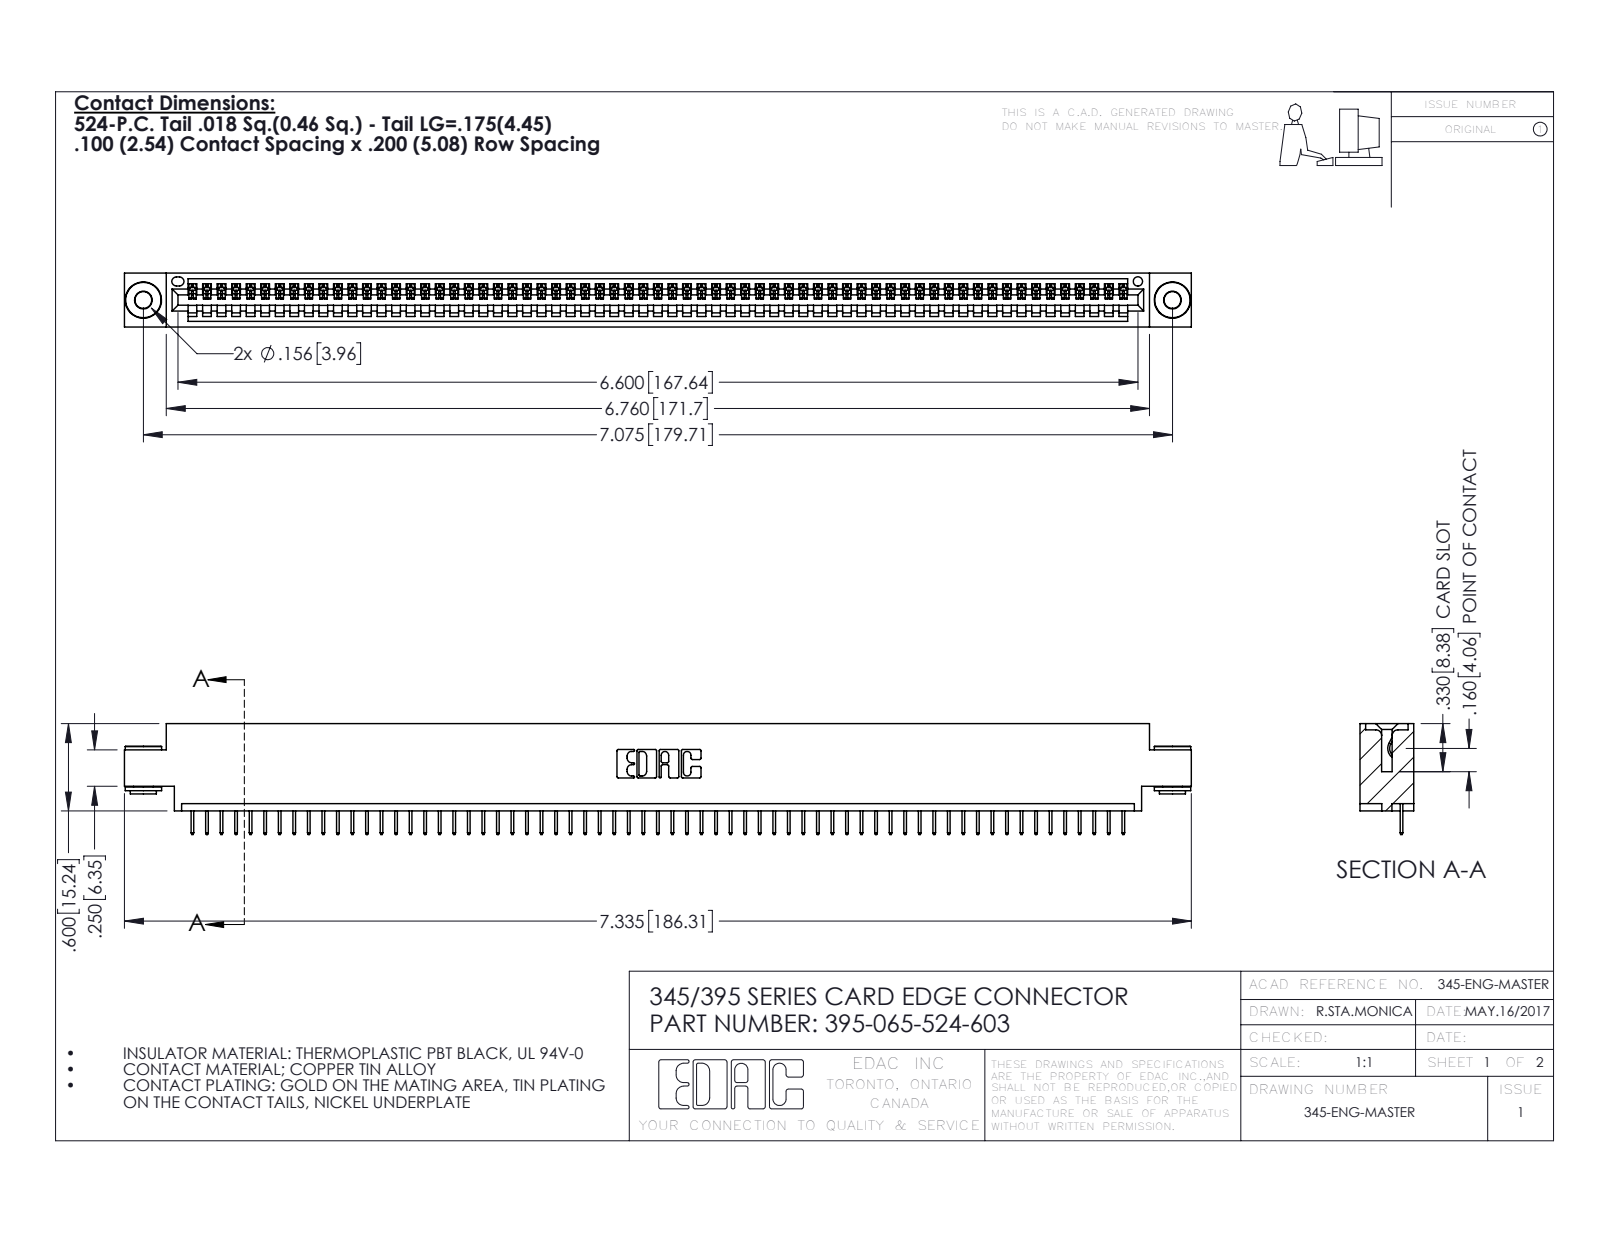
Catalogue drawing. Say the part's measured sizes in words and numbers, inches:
The part is named "345 Part_0.170 Offset - 0.156 Dia-TH; 345-250-002_345-250-002-102; 395-065-524-603; 345-292-001_345-293-124". Its 3-D file was written by "SolidWorks 2016 (CONFIG_CONTROL_DESIGN)". It is 68 solids with 4198 faces: 3084 planar, 1106 cylindrical and 8 other. Overall it measures 7.335 by 0.762 by 0.37 inches. Its volume is 1.07 cubic inches and its surface area 35.86 square inches. Round holes: 2 of diameter 0.116, 2 of diameter 0.156, 1 of diameter 0.064. Round bosses or shafts: 2 of diameter 0.25, 2 of diameter 0.18, 2 of diameter 0.136. Partial cylindrical surfaces (rounded edges, fillets, slot ends): 130 of radius 0.006, 22 of radius 0.01, 6 of radius 0.007, 6 of radius 0.031, 3 of radius 0.026, 2 of radius 0.031, 2 of radius 0.04, 1 of radius 0.014. The main face-to-face distances are 0.072, 0.298, 0.37, 0.2, 0.098, 0.272, 0.025, 0.225, 0.072, 0.175. The hole center spacings are 0.27, 6.839, 7.075.
